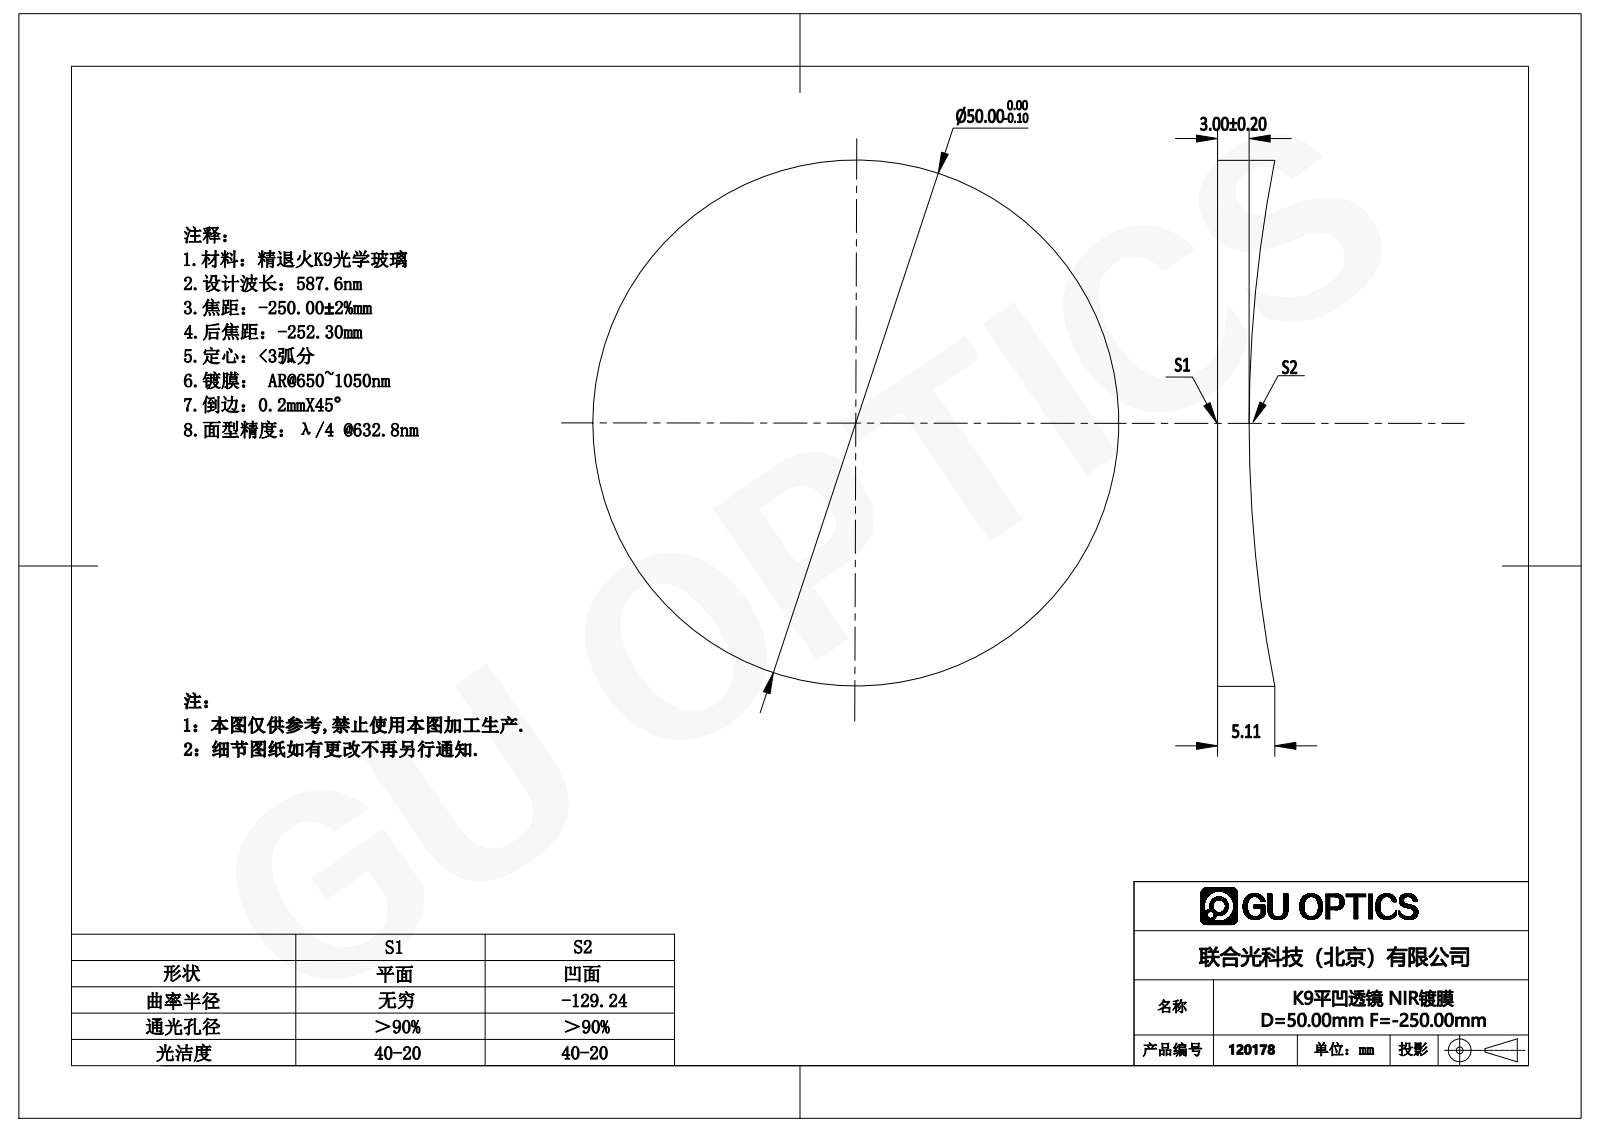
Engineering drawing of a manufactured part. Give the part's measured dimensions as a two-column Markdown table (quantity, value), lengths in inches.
| quantity | value |
| --- | --- |
| part name | 120058 |
| STEP written by | SolidWorks 2016 (AUTOMOTIVE_DESIGN) |
| units | inches |
| bodies | 1 solid, 5 faces (1 planar, 2 cylindrical, 2 other) |
| overall size | 1.969 × 1.969 × 0.214 |
| volume | 0.505 in³ |
| surface area | 7.44 in² |
| round bosses / shafts (diameter × count) | 1.969 × 1 |
